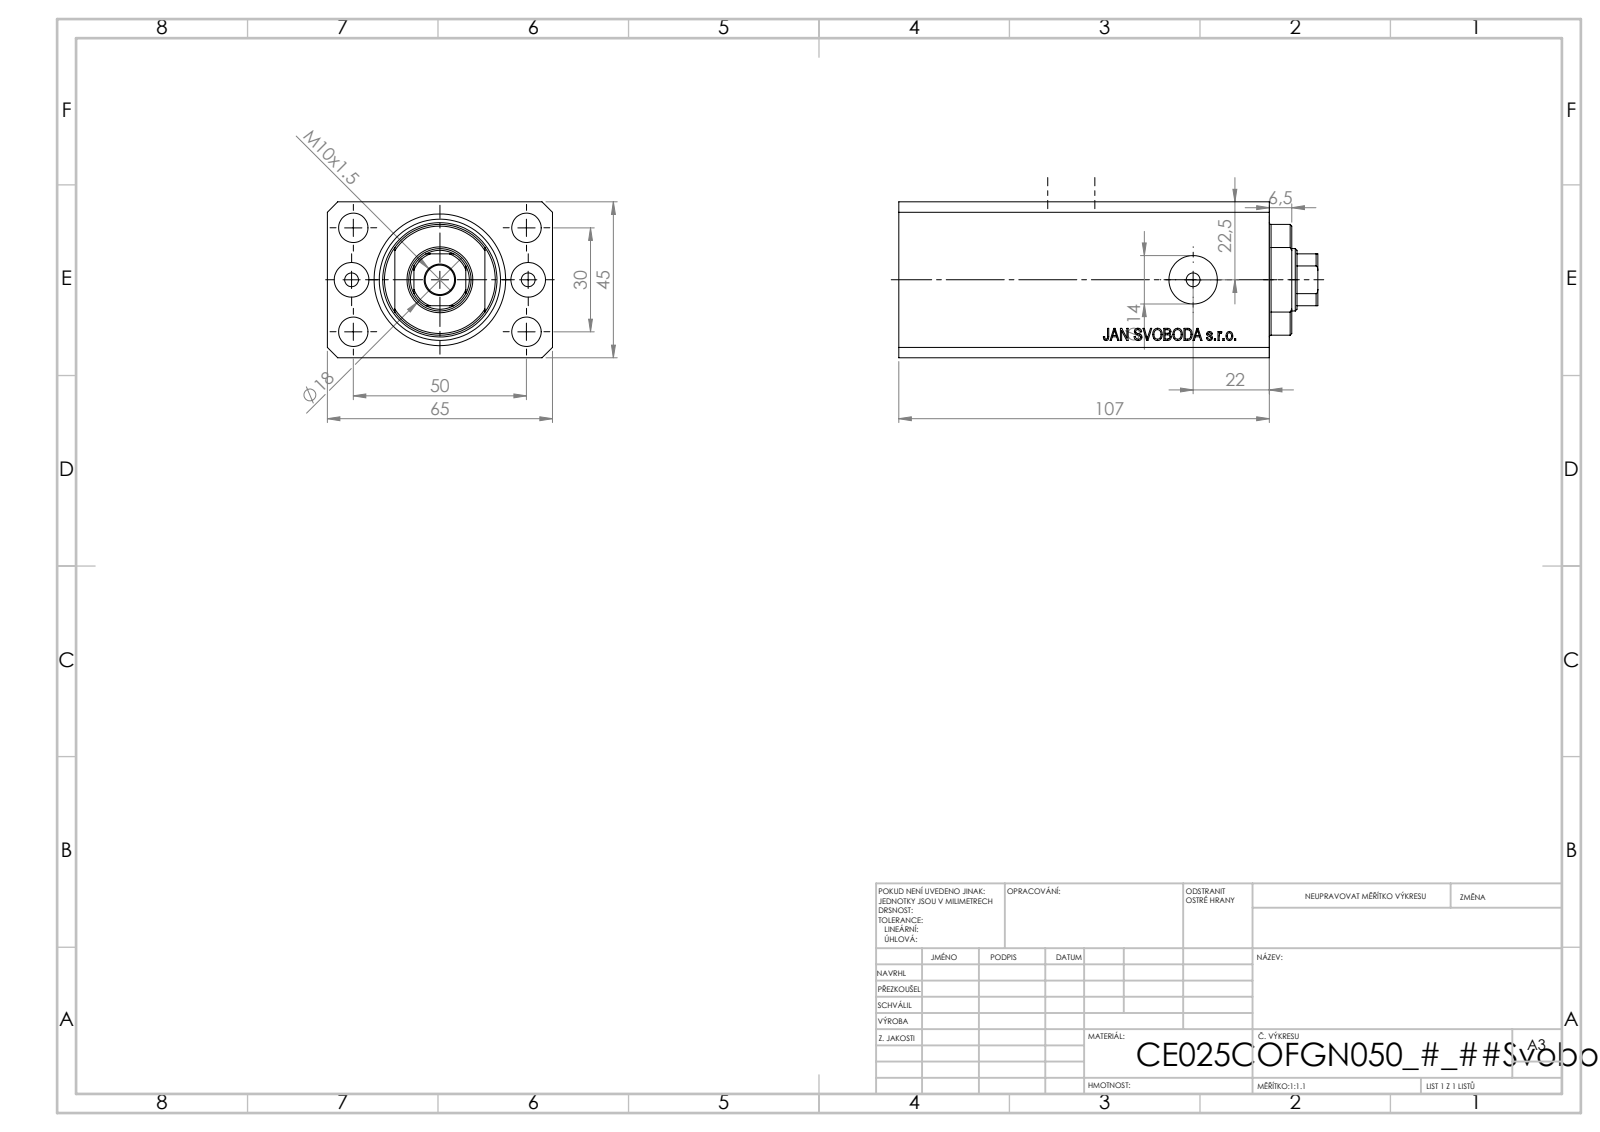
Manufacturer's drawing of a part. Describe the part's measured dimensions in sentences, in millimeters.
The part is named "V250CE_C_VCP; V250CE_C_Body; V250CE_VC_C". Its 3-D file was written by "SolidWorks 2019 (CONFIG_CONTROL_DESIGN)". It is 3 solids with 864 faces: 428 planar, 44 cylindrical and 392 other. Overall it measures 121 by 65 by 45 millimeters. Its volume is 277 187 cubic millimeters and its surface area 63 985 square millimeters. Round holes: 5 of diameter 8.5, 4 of diameter 4, 2 of diameter 10, 2 of diameter 14, 1 of diameter 18, 1 of diameter 25, 1 of diameter 38. Partial cylindrical surfaces (rounded edges, fillets, slot ends): 1 of radius 8.5, 1 of radius 16. The main face-to-face distances are 45, 65, 14, 93, 107, 6.9, 86.1, 100.1, 73.52, 20.5. The hole center spacings are 15.01, 29.15, 52.68, 25.5, 30, 50, 58.31, 51.
